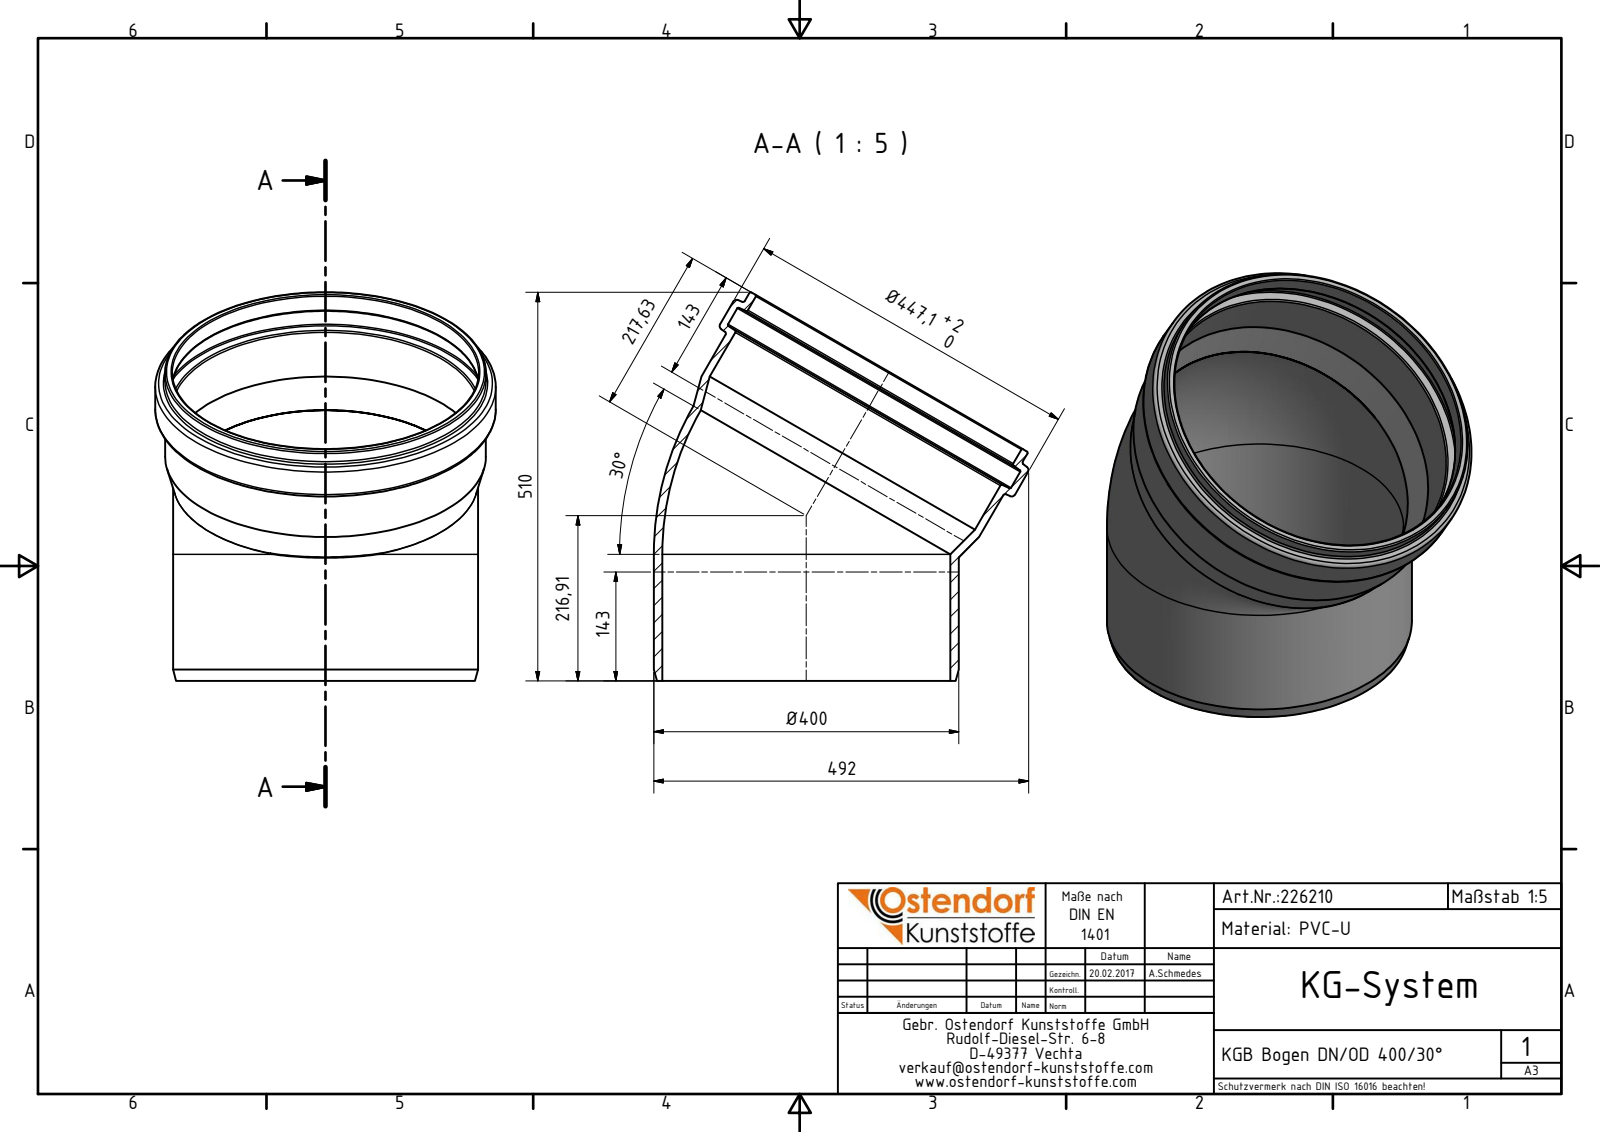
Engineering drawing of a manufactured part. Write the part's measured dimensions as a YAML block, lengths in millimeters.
part_name: "226210 KGB Bogen DN_OD 400_30°"
step_written_by: "Autodesk Inventor 2016 (AUTOMOTIVE_DESIGN)"
units: millimeters
bodies: {solids: 1, faces: 32, planar: 3, cylindrical: 8, other: 21}
overall_size: [510, 492, 447.1]
volume: 5762000
surface_area: 1159000
round_holes:
  - {diameter: 378.35, count: 1}
  - {diameter: 402, count: 1}
  - {diameter: 402.4, count: 1}
  - {diameter: 429.1, count: 1}
round_bosses_or_shafts:
  - {diameter: 447.1, count: 1}
  - {diameter: 421.4, count: 1}
  - {diameter: 421.1, count: 1}
  - {diameter: 400.35, count: 1}
face_to_face_distances: [167.19]
